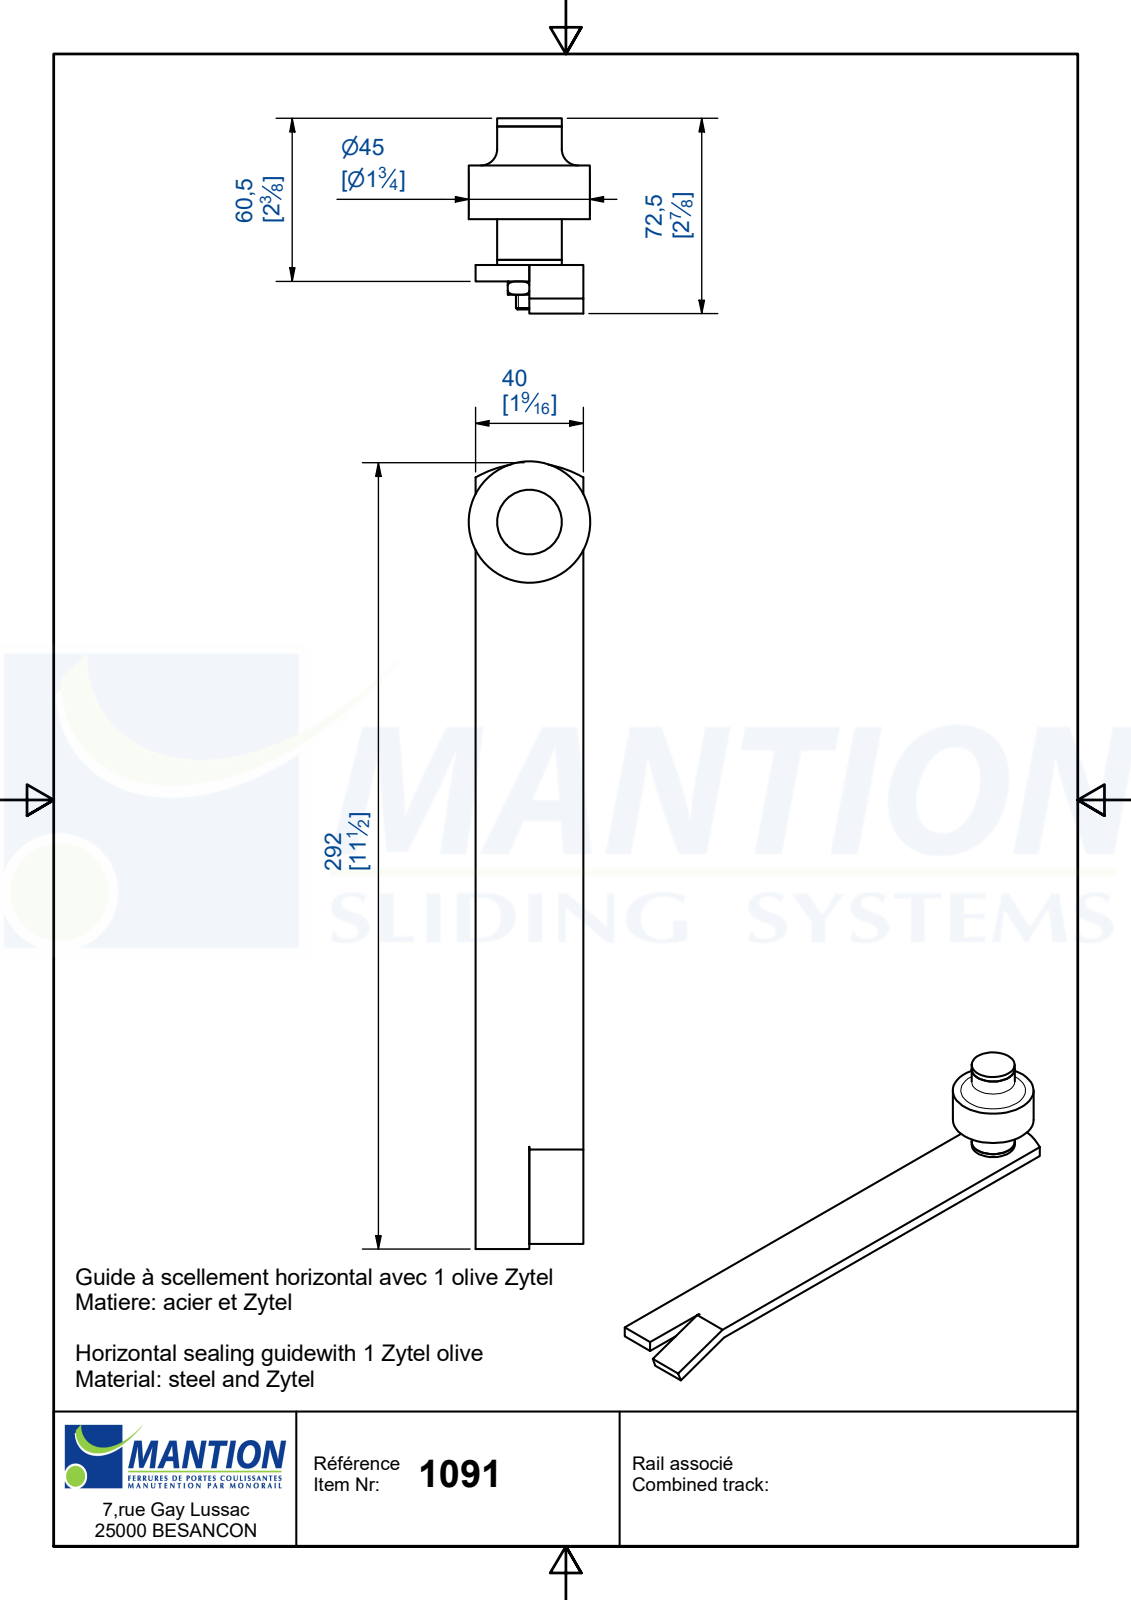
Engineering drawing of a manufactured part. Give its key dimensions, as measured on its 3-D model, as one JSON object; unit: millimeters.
{"part_name": "1091; 14596; 16715; 1093 (+2 more)", "step_written_by": "Autodesk Inventor 2017 (AUTOMOTIVE_DESIGN)", "units": "millimeters", "bodies": {"solids": 5, "faces": 76, "planar": 49, "cylindrical": 19, "other": 8}, "overall_size": [292.5, 72.5, 45], "volume_mm3": 110634, "surface_area_mm2": 47787, "round_holes": [[8.38, 1], [12, 1], [12.1, 1], [17, 1], [34, 1]], "round_bosses_or_shafts": [[45, 1], [24, 1], [16, 1], [11.8, 1], [10, 1]], "partial_cylinders_radius": [[40, 1]], "face_to_face_distances": [6, 40, 17, 20, 17.5, 3, 23, 2, 43, 37]}
